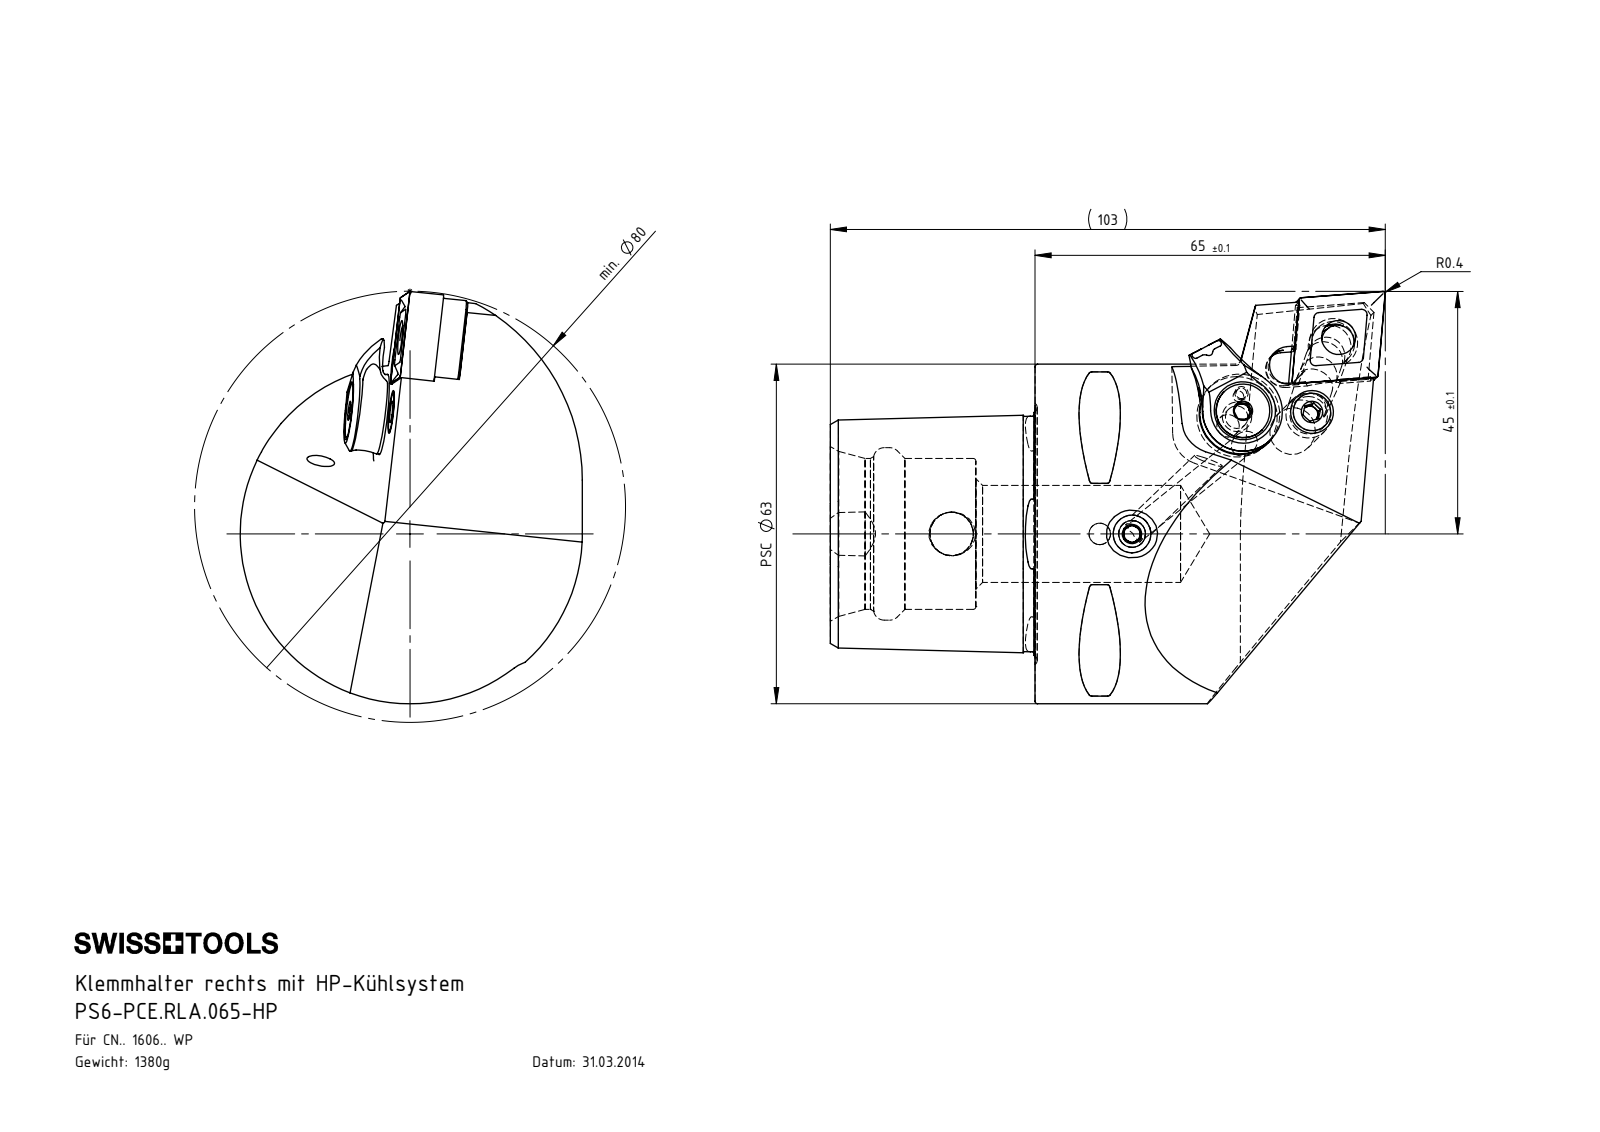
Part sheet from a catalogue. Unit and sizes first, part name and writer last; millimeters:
Units: millimetres
Overall size (bounding box): 103 × 76.5 × 64
Round holes (diameter × count): ⌀4.2 ×2, ⌀5 ×2, ⌀7 ×2, ⌀1.2 ×1, ⌀2 ×1, ⌀2.5 ×1, ⌀3 ×1, ⌀4 ×1, ⌀5.2 ×1, ⌀6.35 ×1, ⌀8.05 ×1, ⌀8.1 ×1
Round bosses / shafts (diameter × count): ⌀8 ×2, ⌀63 ×1, ⌀15 ×1, ⌀13.4 ×1, ⌀10 ×1, ⌀7.9 ×1, ⌀6.4 ×1, ⌀6 ×1
Partial cylindrical surfaces — rounded edges, fillets, slot ends (radius × count): R0.5 ×10, R0.4 ×4, R1.5 ×4, R3.5 ×4, R0.3 ×2, R3.1 ×1, R3.75 ×1, R4 ×1
Main face-to-face distances: 38, 6.05, 24.88, 1.55, 4.76, 10.81, 6.31, 4.5, 11, 27
Hole centre spacings: 4.5, 12.06, 23.71, 23.97, 4.51, 11.33, 11.34, 14.76
Volume: 184 169 mm³ · Surface area: 35 462 mm²
Bodies: 10 solids, 441 faces (131 planar, 115 cylindrical, 195 other)
Part name (STEP PRODUCT): WCE-ER2.101.004_A; CHP-ER1.015.006; WCE-ER3.101.000_A; PS6-PCE.RLA.065-HP_B (+8 more)
STEP written by: SolidWorks 2017 (AUTOMOTIVE_DESIGN)
